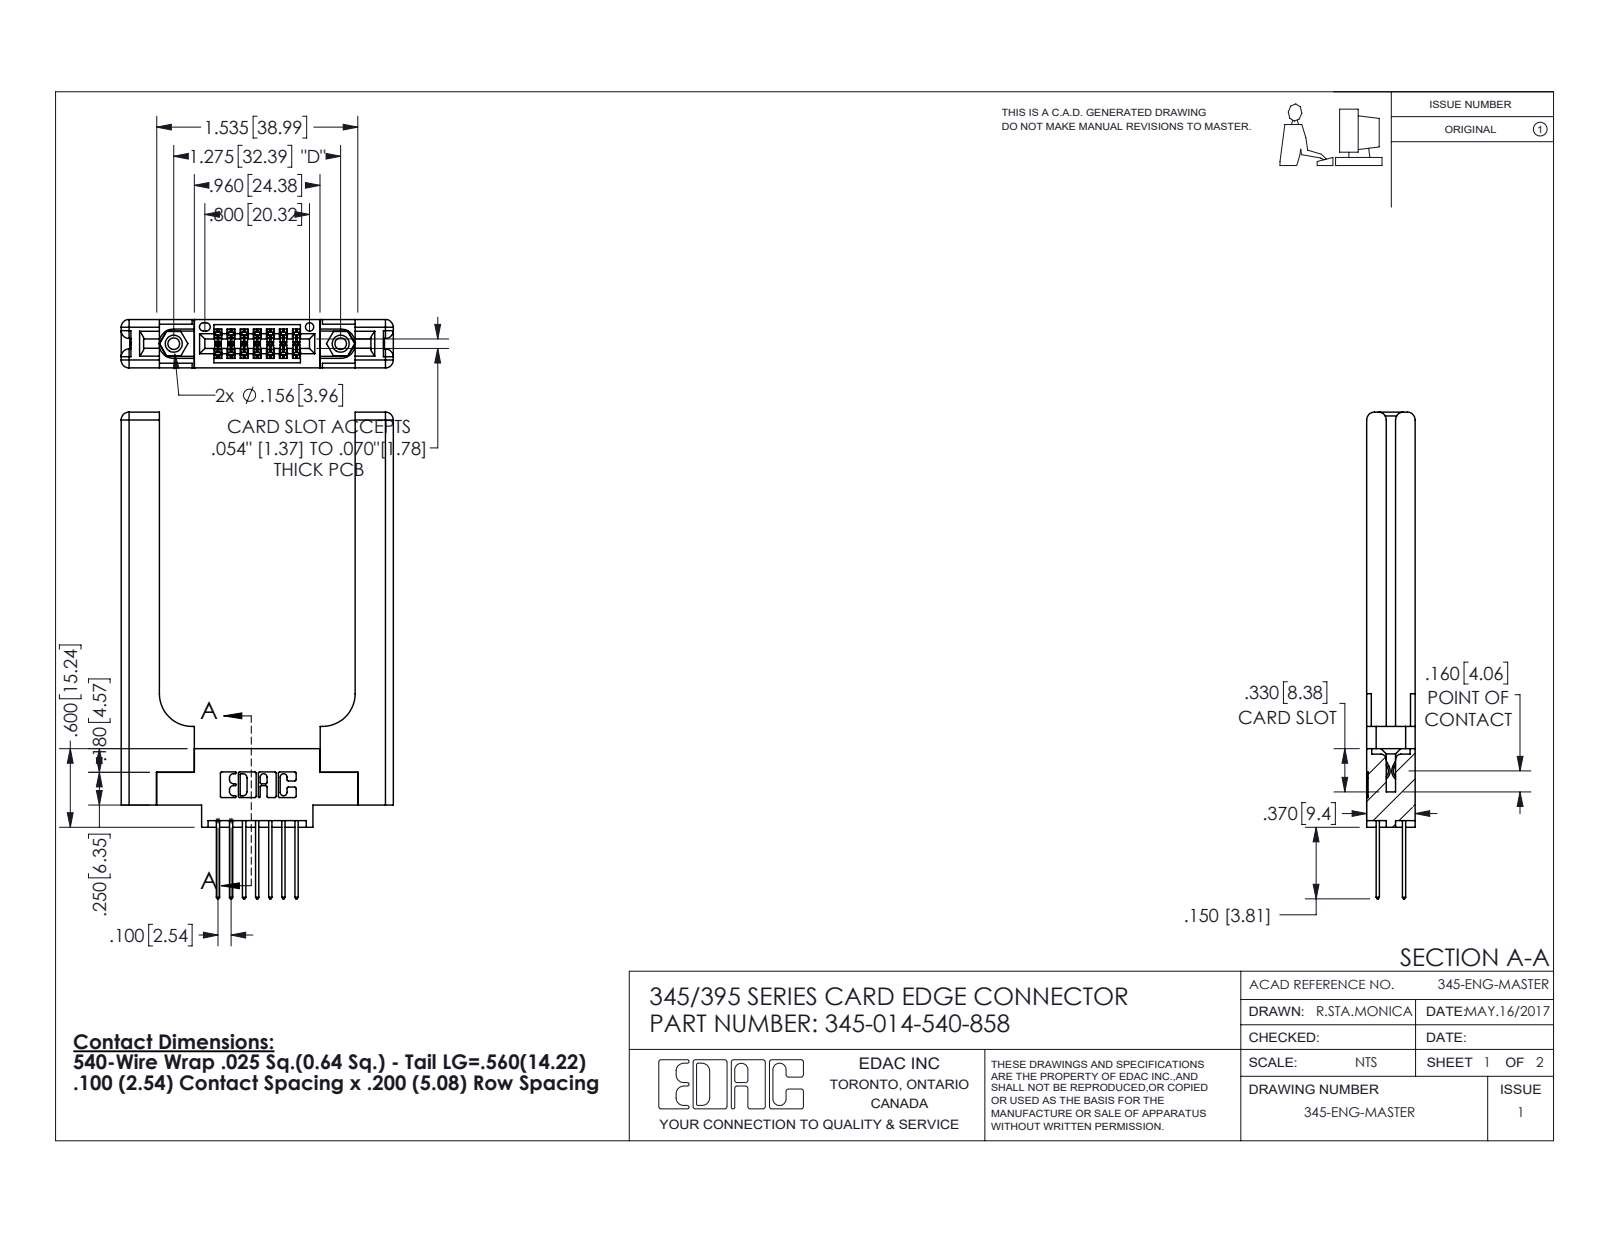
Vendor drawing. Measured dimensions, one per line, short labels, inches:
name: 345-220-058_345-220-058; 345-292-001_345-293-140; 345 Part_0.170 Offset - 0.156 Dia-TH; 345-014-540-858 (+1 more)
written by: SolidWorks 2016 (CONFIG_CONTROL_DESIGN)
unit: in
bodies: 19 solids, 1086 faces (694 planar, 332 cylindrical, 60 other)
size: 3.717 × 2.079 × 0.37
volume: 0.807 in³; area: 18.27 in²
holes: 2× ⌀0.089, 2× ⌀0.125, 2× ⌀0.156, 1× ⌀0.064
bosses: 2× ⌀0.155
rounds: 22× R0.01, 21× R0.006, 16× R0.06, 14× R0.01, 6× R0.007, 6× R0.031, 3× R0.026, 2× R0.014
face distances: 0.37, 0.15, 0.072, 0.22, 0.148, 0.077, 0.298, 1.496, 0.225, 0.071
hole spacings: 0.27, 1.045, 1.275
